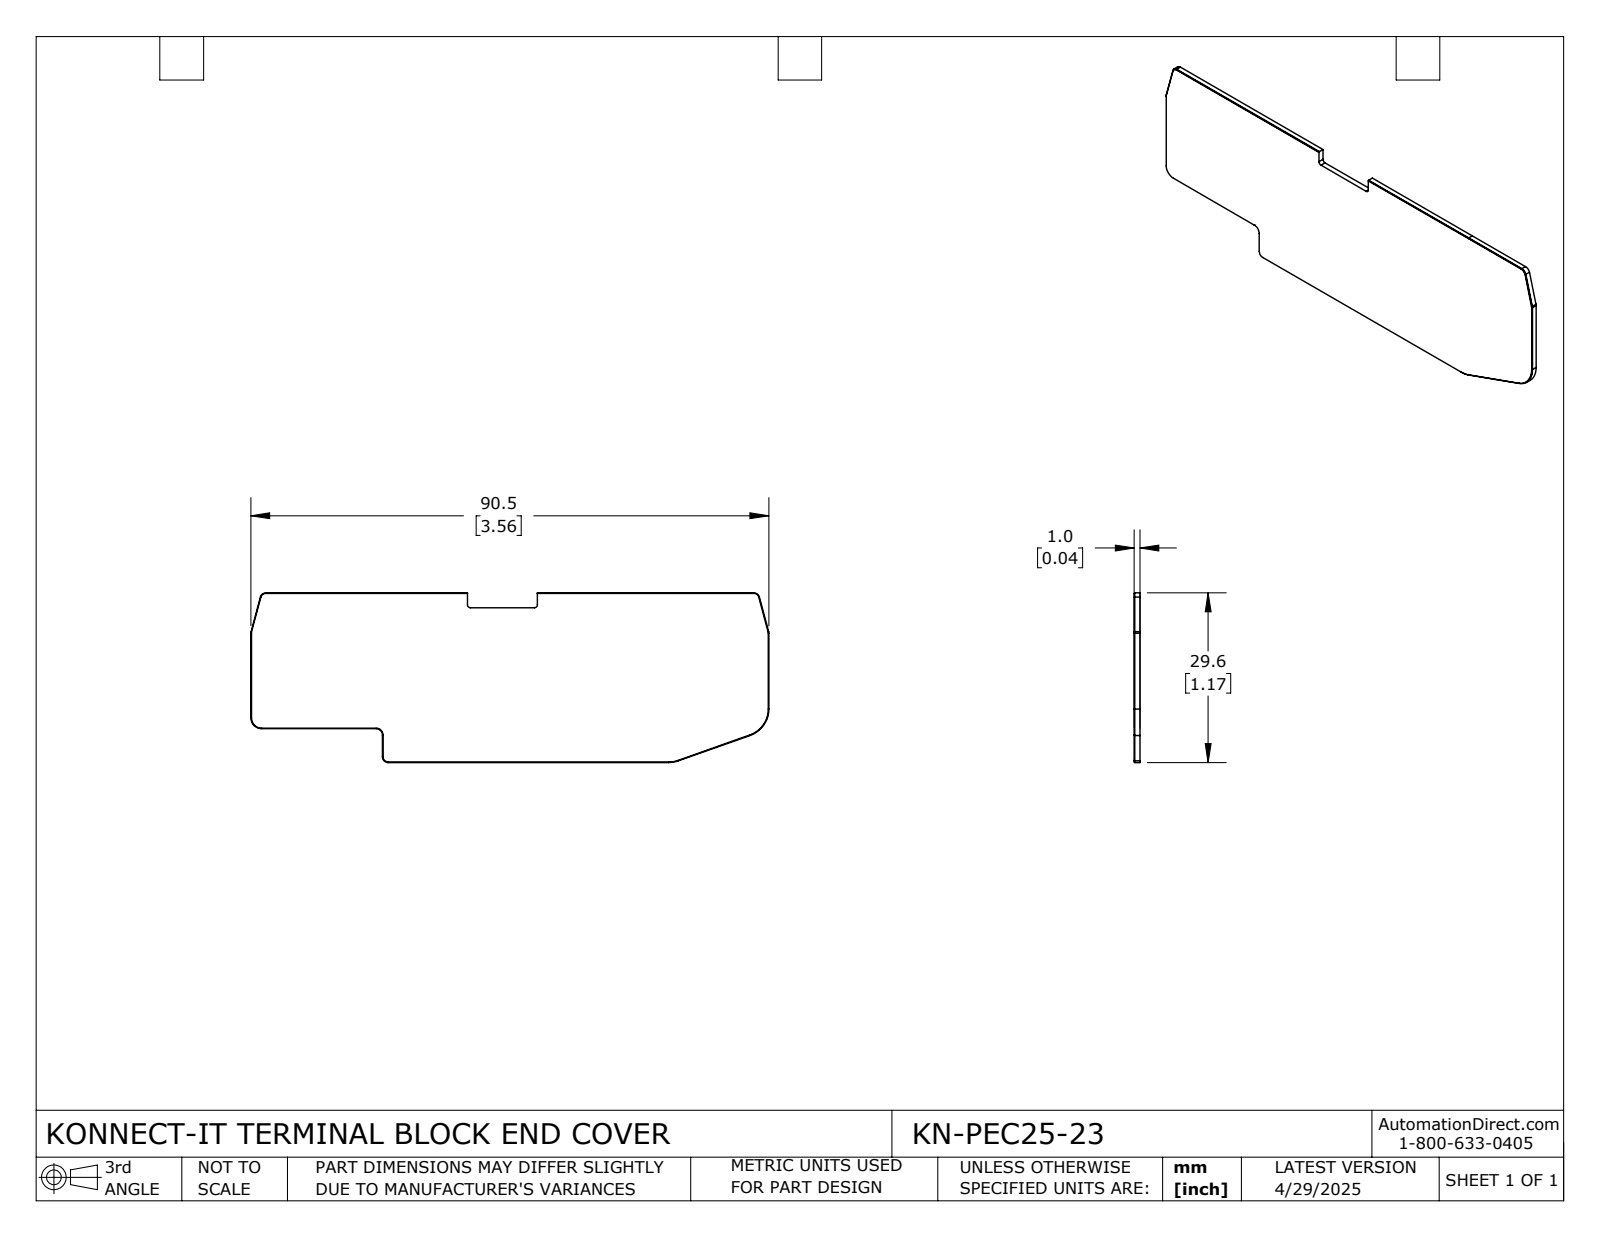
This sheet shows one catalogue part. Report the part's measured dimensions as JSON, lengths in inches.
{"part_name": "KN-PEC25-23", "step_written_by": "SolidWorks 2024 (CONFIG_CONTROL_DESIGN)", "units": "inches", "bodies": {"solids": 1, "faces": 48, "planar": 28, "cylindrical": 20, "other": 0}, "overall_size": [3.561, 1.166, 0.039], "volume_in3": 0.149, "surface_area_in2": 7.947, "partial_cylinders_radius": [[0.035, 5], [0.039, 5], [0.02, 2], [0.193, 2], [0.043, 1], [0.047, 1], [0.071, 1], [0.075, 1]], "face_to_face_distances": [0.039, 1.166, 0.035, 0.232, 0.934, 1.162, 3.561, 1.064, 0.832, 0.102]}
